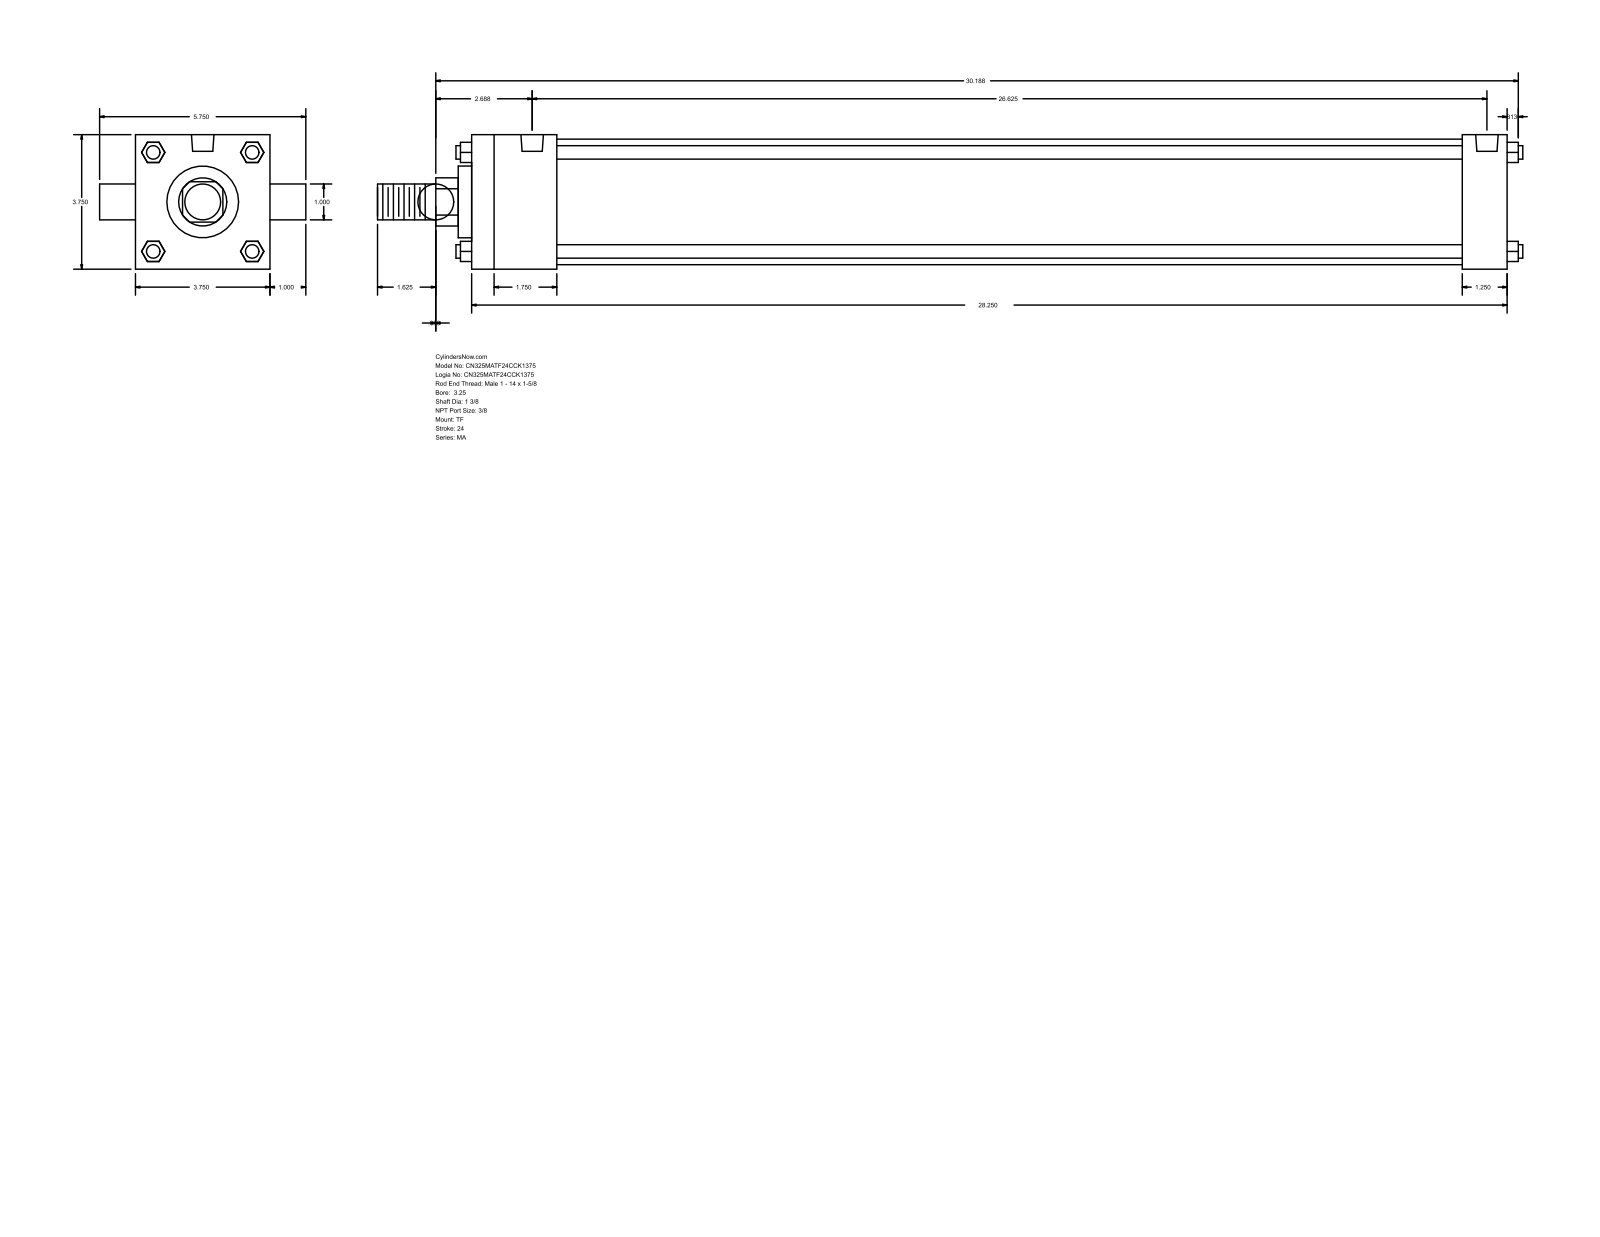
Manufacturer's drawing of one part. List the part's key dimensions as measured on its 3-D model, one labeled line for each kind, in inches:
Part name (STEP PRODUCT): MA_TF__0325_1.375
STEP written by: GSSL Pune (CONFIG_CONTROL_DESIGN)
Units: inches
Bodies: 0 solids, 120 faces (92 planar, 28 cylindrical, 0 other)
Overall size (bounding box): 31.937 × 5.75 × 3.75
Round holes (diameter × count): ⌀0.437 ×3, ⌀0.627 ×2
Round bosses / shafts (diameter × count): ⌀0.375 ×4, ⌀1 ×2, ⌀3.5 ×1, ⌀2 ×1, ⌀1.375 ×1
Partial cylindrical surfaces — rounded edges, fillets, slot ends (radius × count): R0.672 ×1
Main face-to-face distances: 3.75, 28.875, 2.375, 27.625, 25.25, 26.5, 1.25, 0.375, 2.75, 28
Hole centre spacings: 0.188, 26.437, 26.25, 26.625
